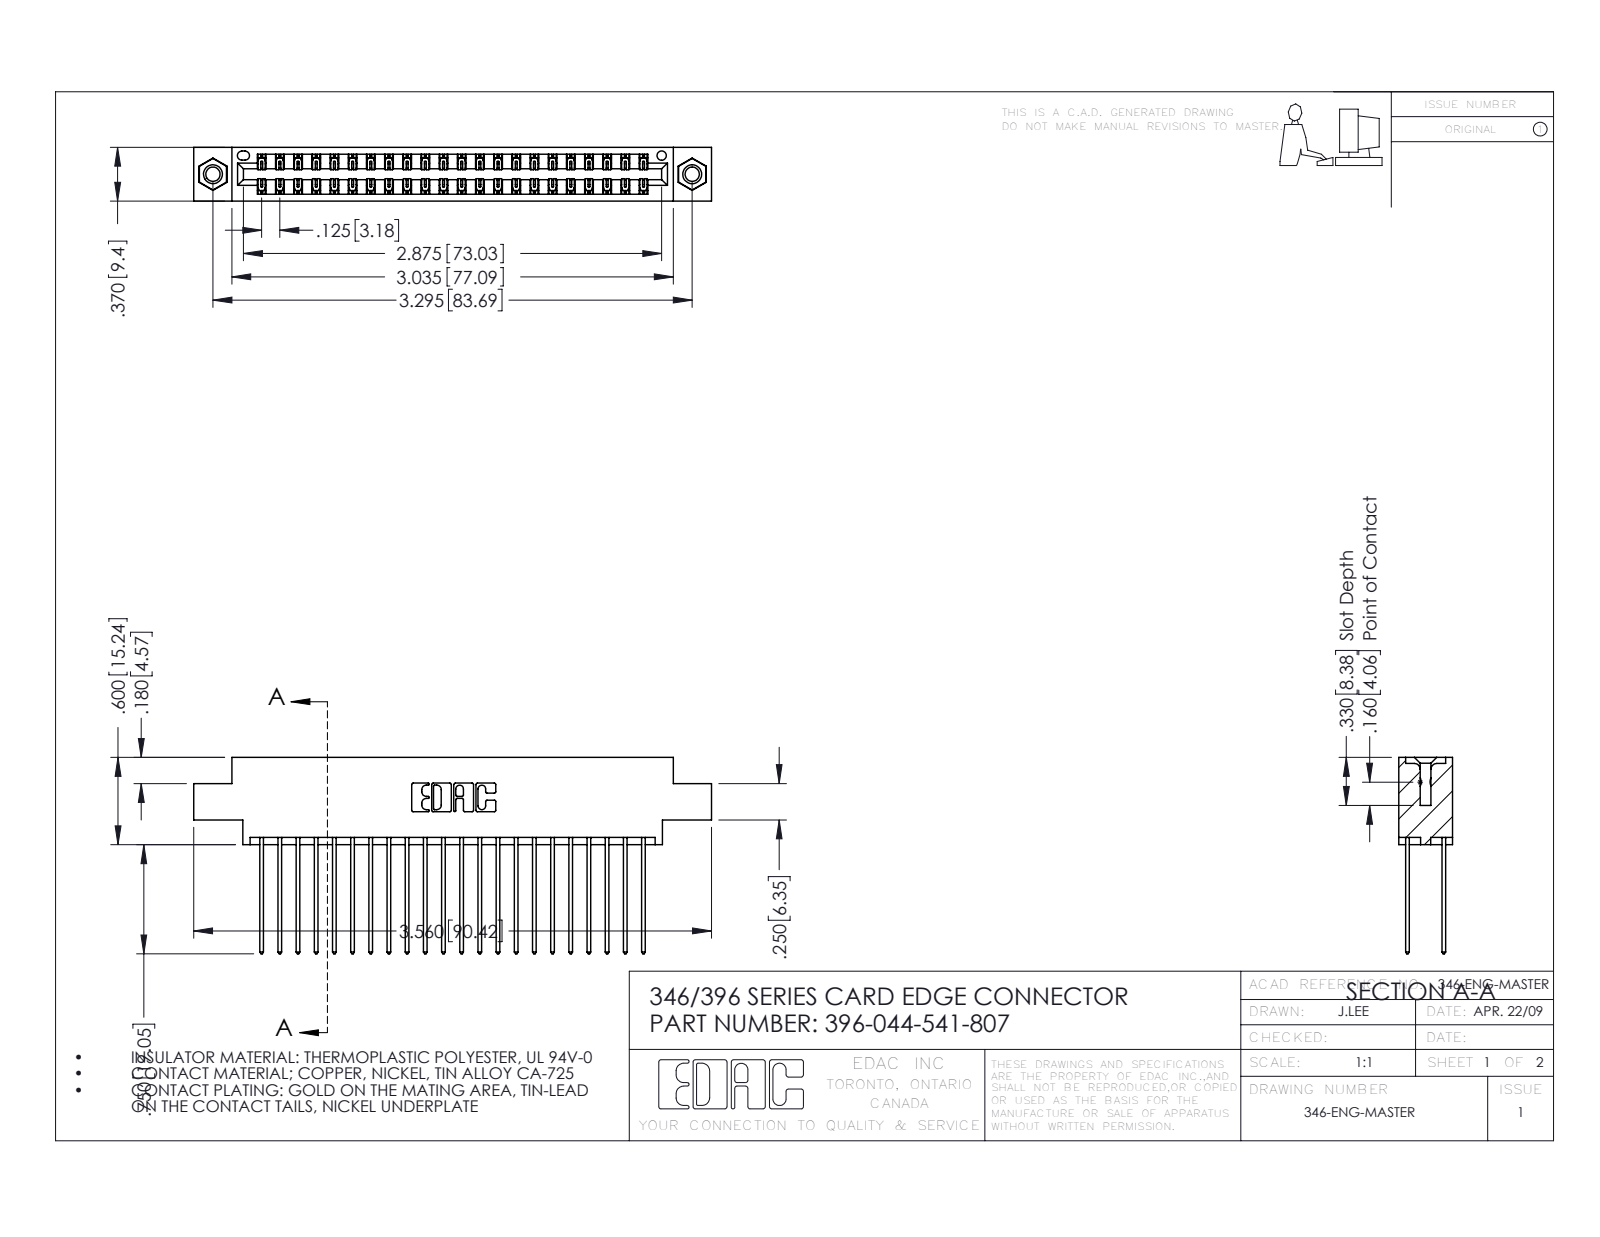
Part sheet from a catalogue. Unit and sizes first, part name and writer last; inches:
Units: inches
Overall size (bounding box): 3.56 × 1.35 × 0.37
Round holes (diameter × count): ⌀0.098 ×2, ⌀0.125 ×2, ⌀0.156 ×2, ⌀0.064 ×1
Round bosses / shafts (diameter × count): ⌀0.155 ×2
Partial cylindrical surfaces — rounded edges, fillets, slot ends (radius × count): R0.006 ×66, R0.01 ×44, R0.01 ×22, R0.007 ×6, R0.031 ×6, R0.026 ×3, R0.014 ×2, R0.022 ×2
Main face-to-face distances: 0.048, 0.322, 0.25, 0.072, 0.298, 0.025, 0.37, 0.275, 0.225, 0.222
Hole centre spacings: 0.246, 3.087, 3.295
Volume: 0.534 in³ · Surface area: 20.35 in²
Bodies: 47 solids, 2474 faces (1652 planar, 806 cylindrical, 16 other)
Part name (STEP PRODUCT): 346 Part_0.170 Offset - 0.156 Dia-TI; 396-044-541-807; 345-292-001_345-293-141; 345-250-001_345-250-005-103
STEP written by: SolidWorks 2016 (CONFIG_CONTROL_DESIGN)
